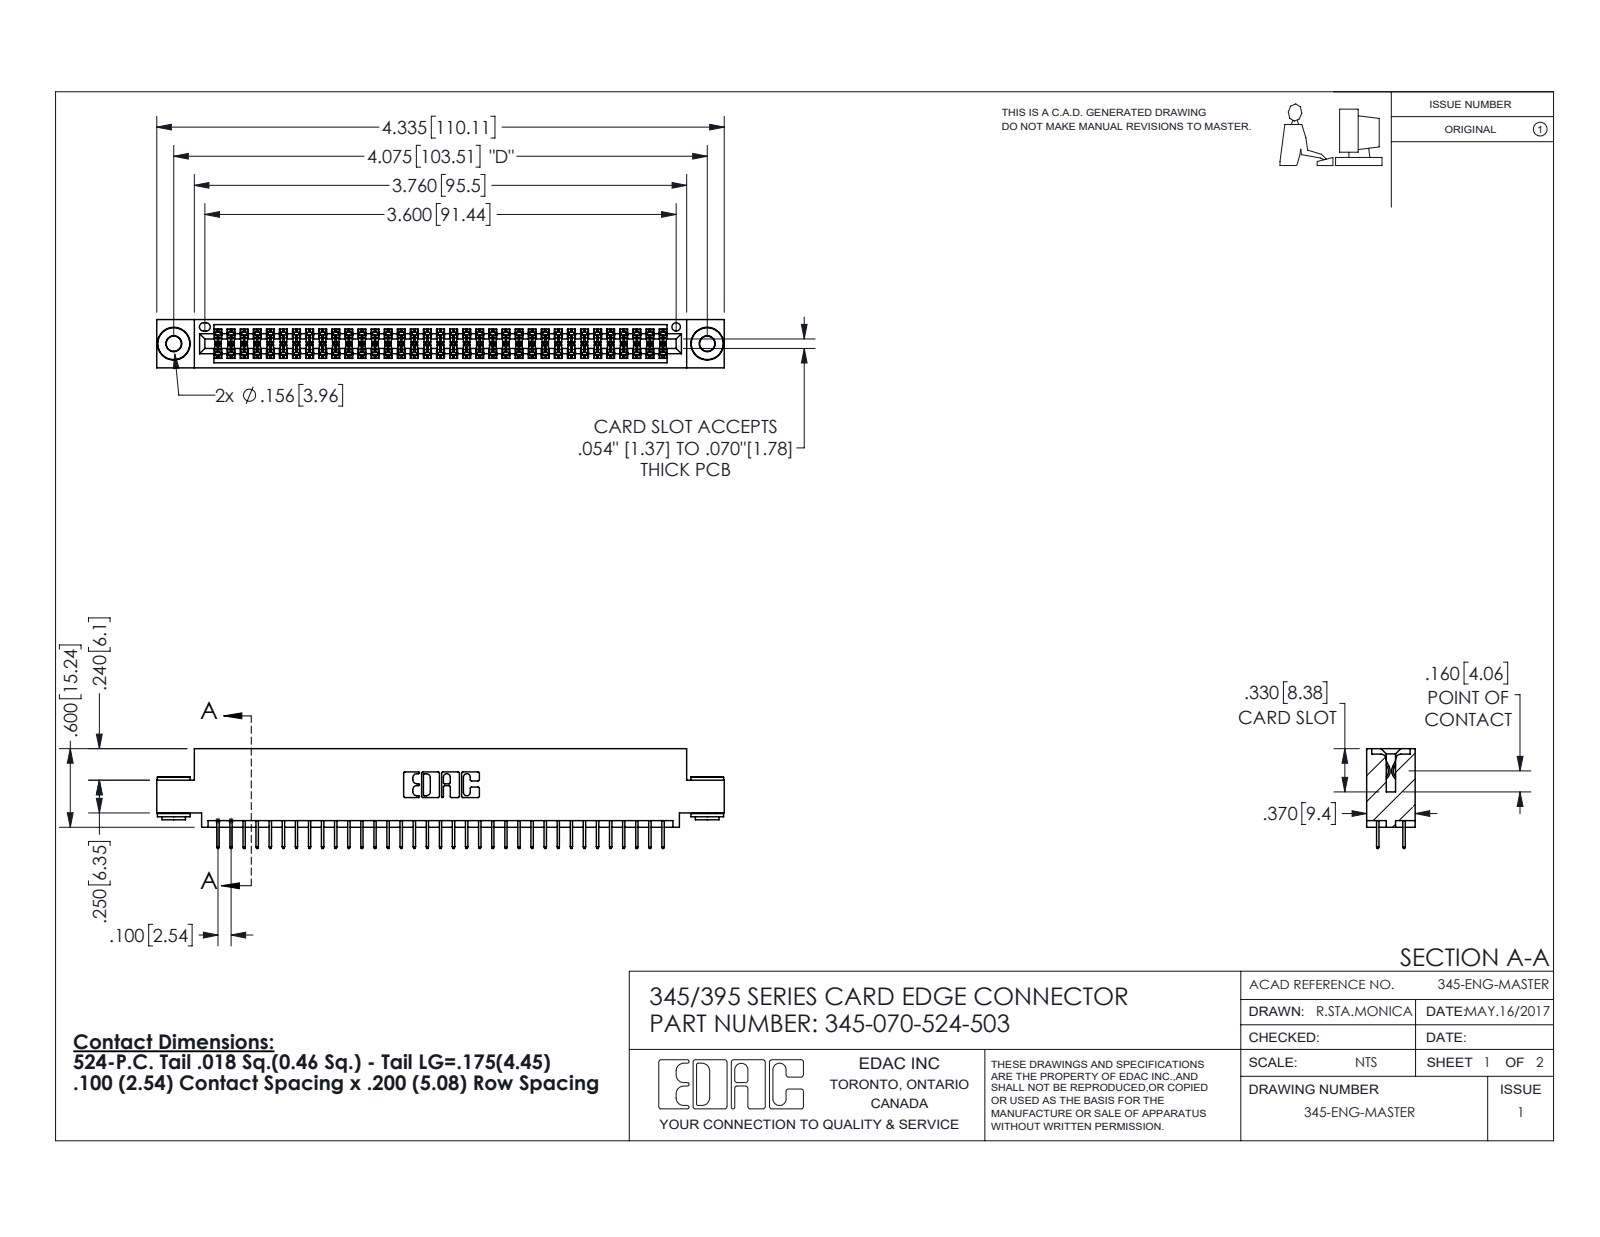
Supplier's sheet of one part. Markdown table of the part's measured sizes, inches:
| quantity | value |
| --- | --- |
| part name | 345-292-001_345-293-124; 345-070-524-503; 345-250-002_345-250-002-102; 345 Part_0.110 Offset - 0.156 Dia-TH |
| STEP written by | SolidWorks 2016 (CONFIG_CONTROL_DESIGN) |
| units | inches |
| bodies | 73 solids, 3948 faces (2824 planar, 1116 cylindrical, 8 other) |
| overall size | 4.335 × 0.762 × 0.37 |
| volume | 0.639 in³ |
| surface area | 23.81 in² |
| round holes (diameter × count) | 0.116 × 2, 0.156 × 2, 0.064 × 1 |
| round bosses / shafts (diameter × count) | 0.25 × 2, 0.18 × 2, 0.136 × 2 |
| partial cylindrical surfaces (radius × count) | 0.006 × 105, 0.01 × 22, 0.007 × 6, 0.031 × 6, 0.026 × 3, 0.014 × 2, 0.019 × 2, 0.022 × 2 |
| main face-to-face distances | 0.072, 0.298, 0.37, 0.2, 0.025, 0.098, 0.272, 0.225, 0.072, 0.175 |
| hole center spacings | 0.27, 3.839, 4.075 |
